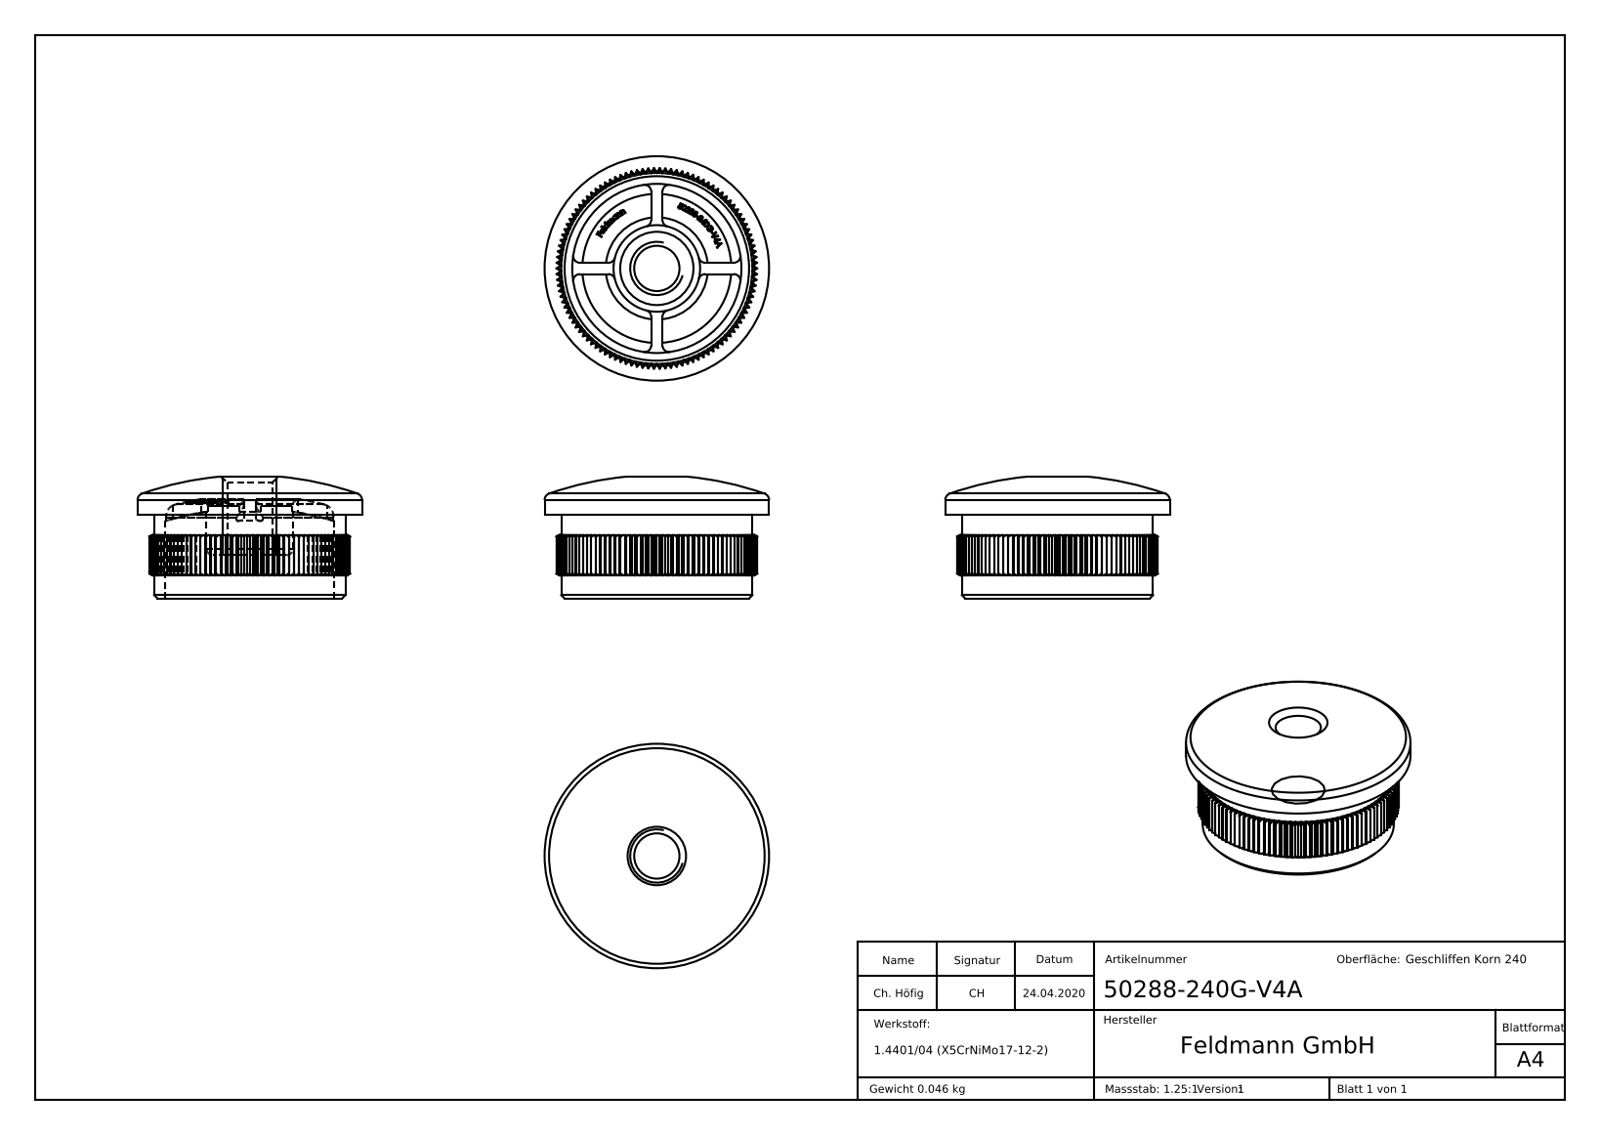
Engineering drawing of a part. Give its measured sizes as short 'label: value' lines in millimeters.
name: 50288-240G-V4A
written by: SolidWorks 2015 (CONFIG_CONTROL_DESIGN)
unit: mm
bodies: 1 solid, 1115 faces (579 planar, 132 cylindrical, 404 other)
size: 33.7 × 33.7 × 18.3
volume: 5 737 mm³; area: 5 428 mm²
holes: 1× ⌀6.8, 1× ⌀25.4
bosses: 1× ⌀33.7, 1× ⌀28.7, 1× ⌀13
rounds: 16× R1, 1× R15.05
face distances: 14.36, 14.34, 12.5, 6, 3, 6.5, 1.7, 9.5, 3.5, 9
